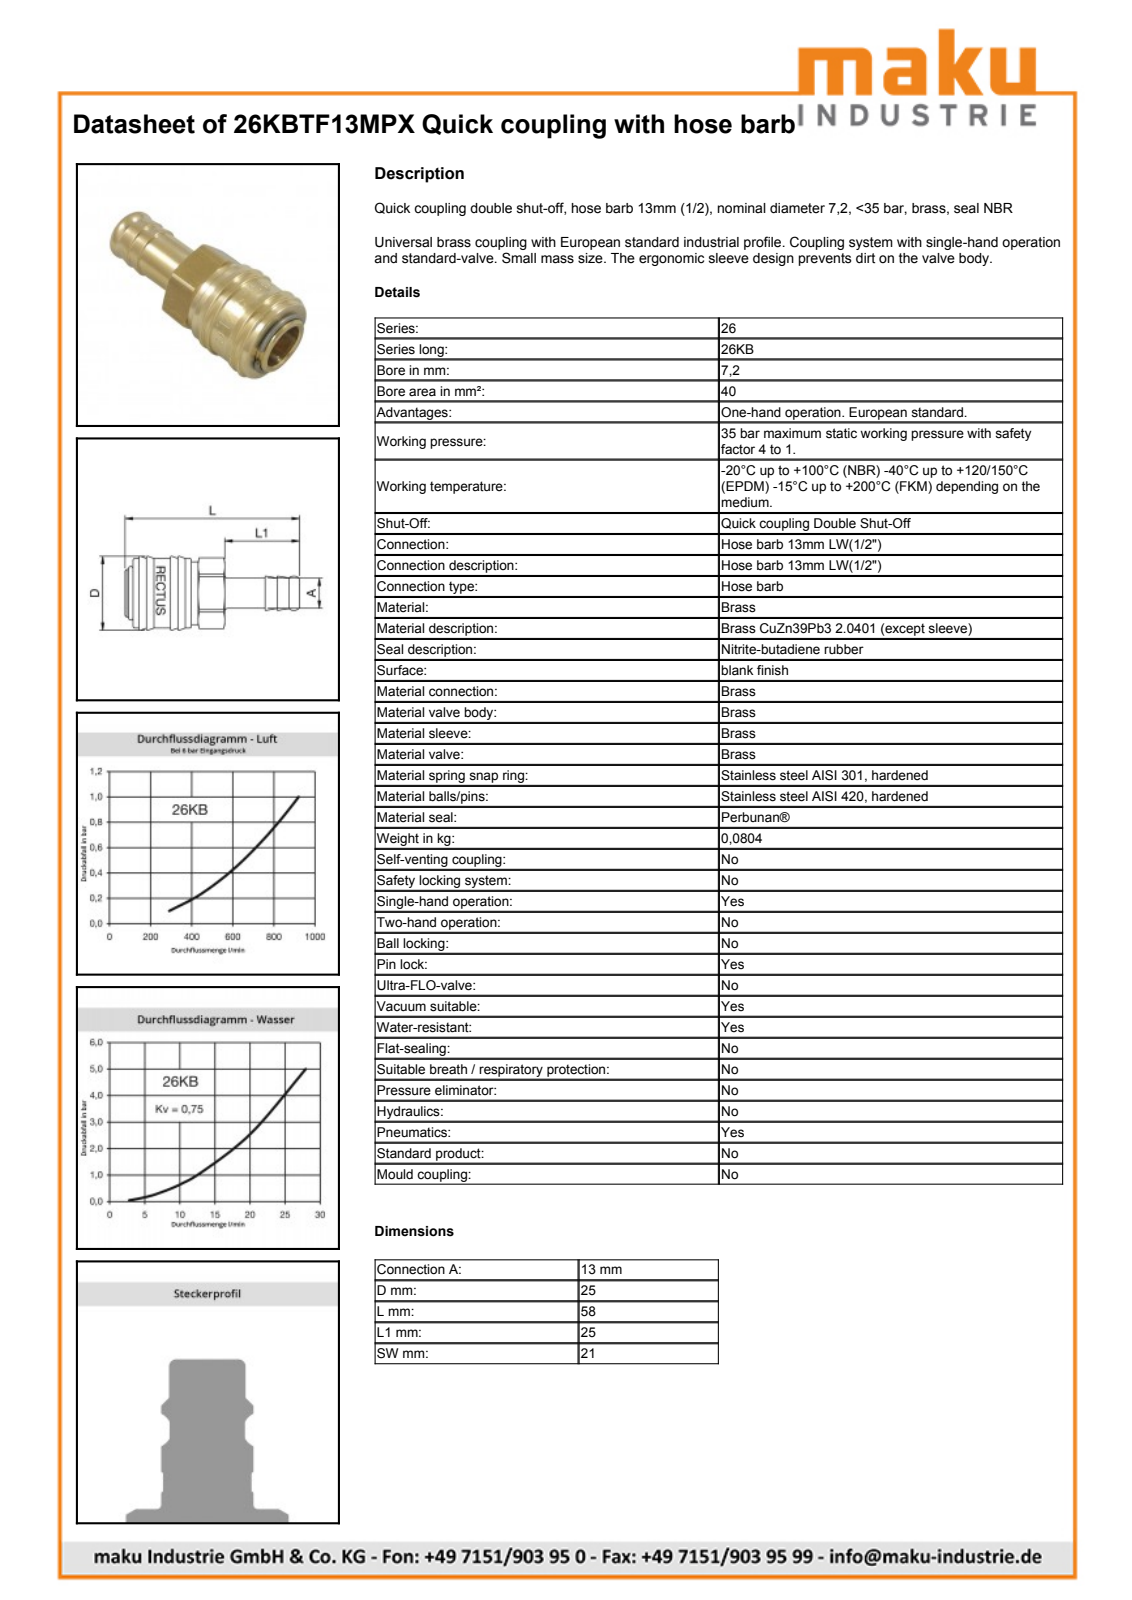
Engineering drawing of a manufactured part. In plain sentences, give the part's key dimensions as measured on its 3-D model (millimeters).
The part is named "D105577". Its 3-D file was written by "Autodesk Inventor 2011 (AUTOMOTIVE_DESIGN)". It is 3 solids with 462 faces: 175 planar, 59 cylindrical and 228 other. Overall it measures 58 by 24.8 by 24.8 millimeters. Its volume is 15 031 cubic millimeters and its surface area 7 676 square millimeters. Round holes: 1 of diameter 16.1, 1 of diameter 17, 1 of diameter 21.1. Round bosses or shafts: 1 of diameter 23.3, 1 of diameter 21, 1 of diameter 18, 1 of diameter 16.65, 1 of diameter 15.95, 1 of diameter 14.95, 1 of diameter 13.1. Partial cylindrical surfaces (rounded edges, fillets, slot ends): 1 of radius 7.9, 1 of radius 11.55, 1 of radius 11.85. The main face-to-face distances are 21, 2.65, 33, 30.35, 58, 55.35, 25, 18.35, 12, 37.
